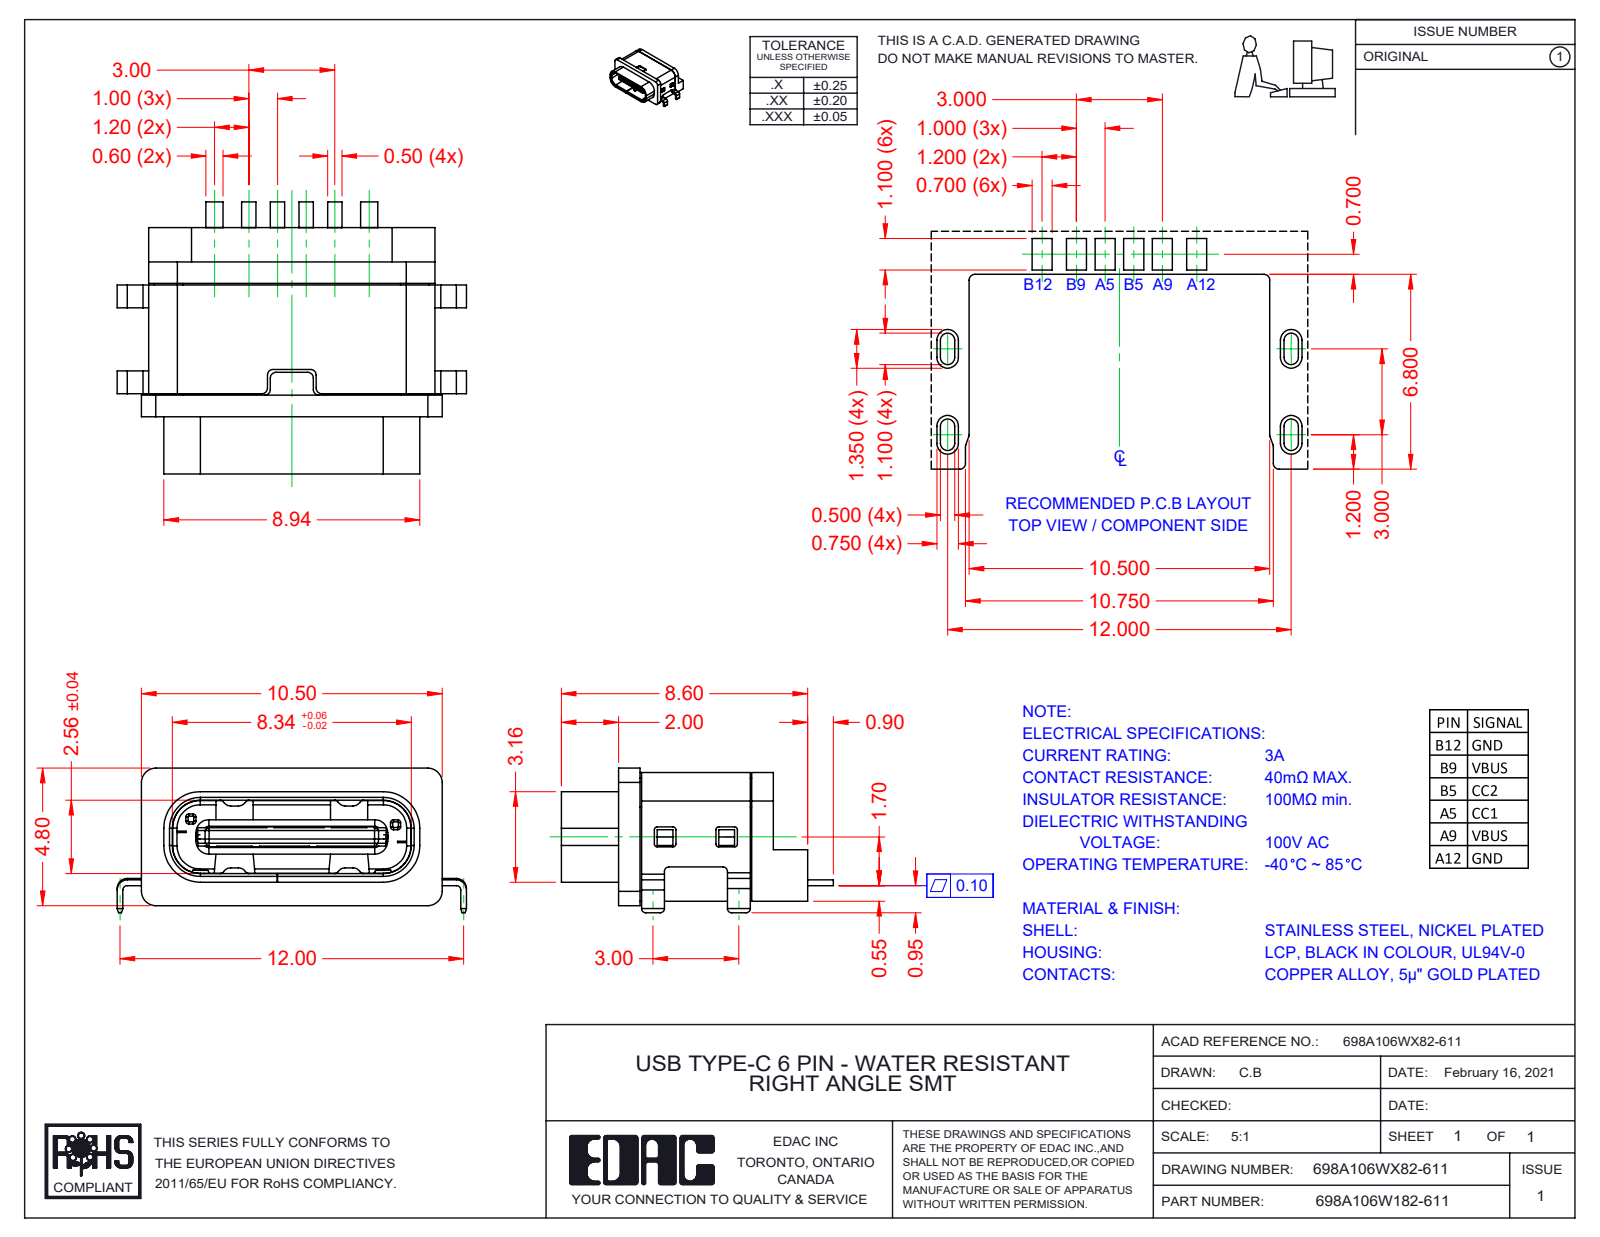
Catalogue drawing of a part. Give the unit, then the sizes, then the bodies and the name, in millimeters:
Units: millimetres
Overall size (bounding box): 12.2 × 9.5 × 5.05
Partial cylindrical surfaces — rounded edges, fillets, slot ends (radius × count): R0.15 ×59, R0.3 ×49, R0.2 ×38, R0.1 ×36, R0.45 ×14, R0.16 ×8, R0.4 ×8, R0.5 ×8
Main face-to-face distances: 0.67, 3.83, 0.97, 3.53, 2.86, 4.3, 3.16, 1.6, 0.47, 3.63
Volume: 235 mm³ · Surface area: 1 161 mm²
Bodies: 11 solids, 1276 faces (896 planar, 329 cylindrical, 51 other)
Part name (STEP PRODUCT): Shell1 698A106WX82-611; Insulator2 698A106WX82-611; Shell2 698A106WX82-611; 698A106W182-611 (+3 more)
STEP written by: SolidWorks 2020 (AUTOMOTIVE_DESIGN)
